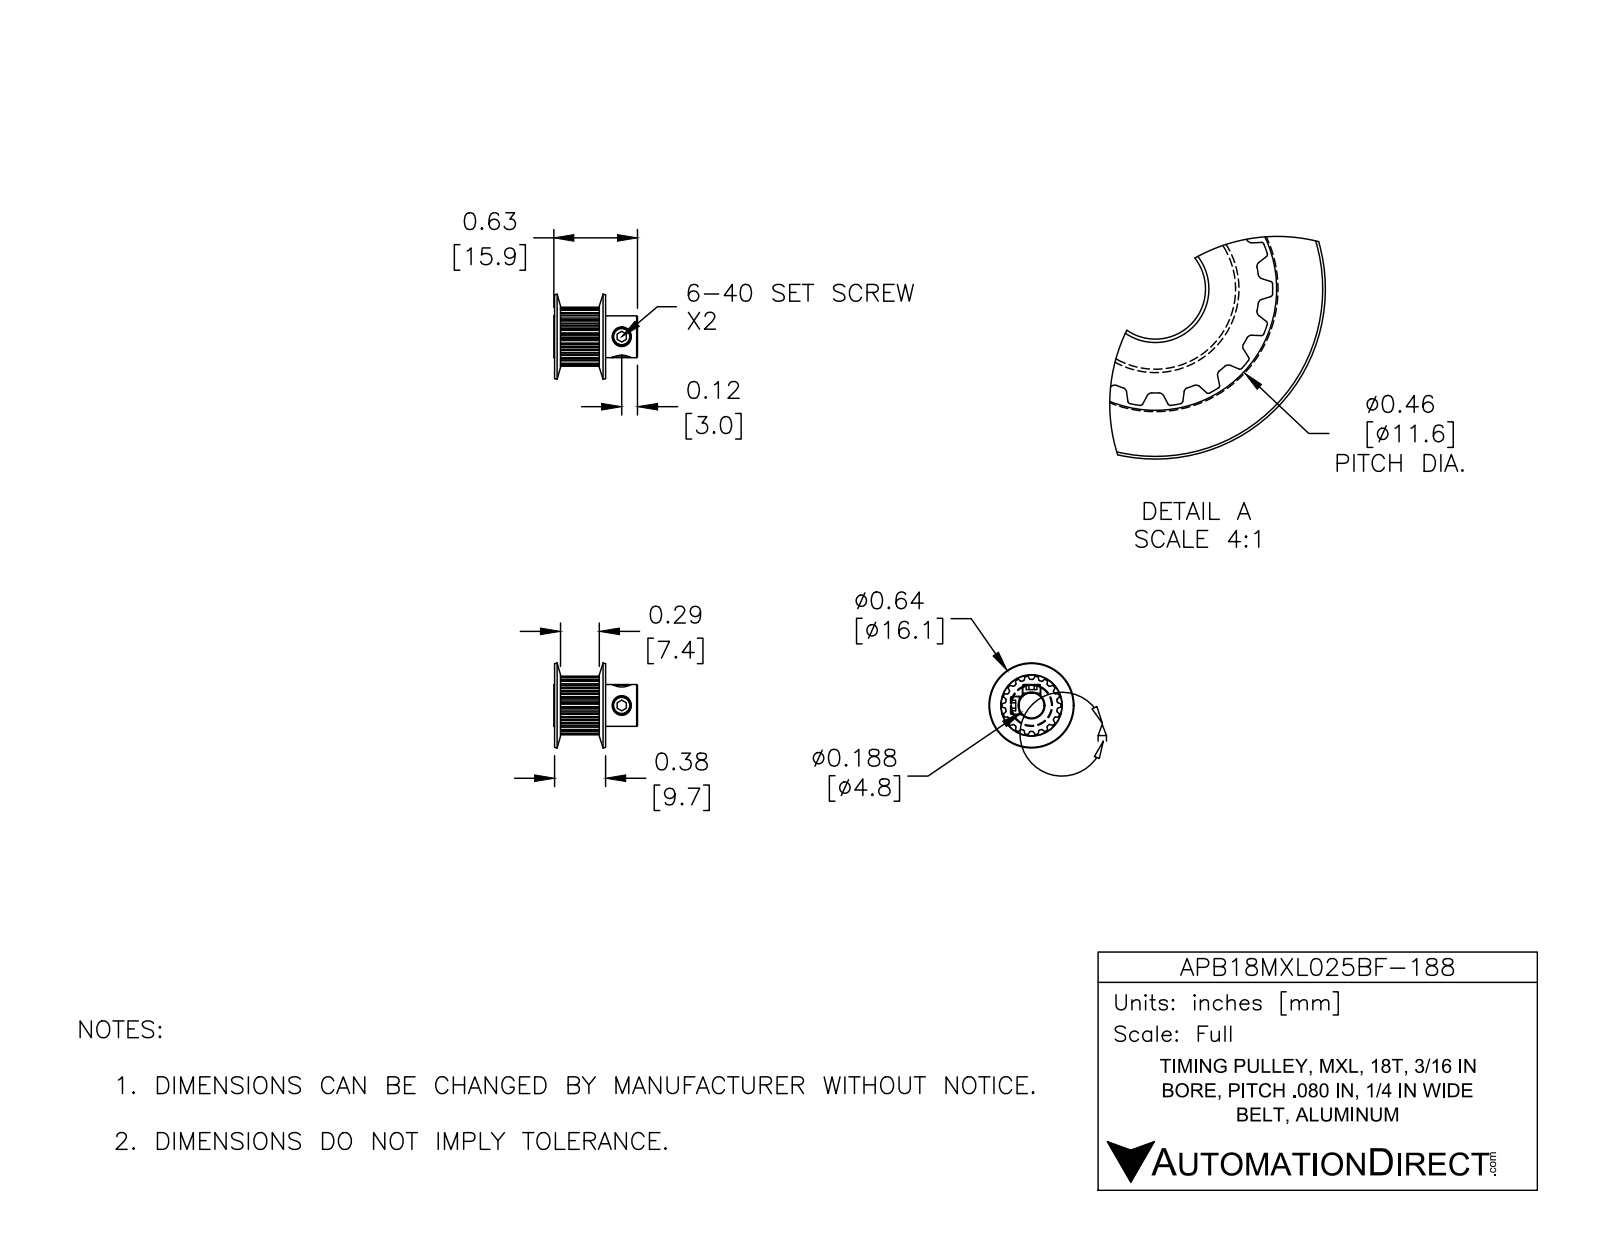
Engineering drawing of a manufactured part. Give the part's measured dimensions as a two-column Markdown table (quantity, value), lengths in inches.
| quantity | value |
| --- | --- |
| part name | APB18MXL025BF-188 |
| STEP written by | SolidWorks 2016 (AUTOMOTIVE_DESIGN) |
| units | inches |
| bodies | 3 solids, 221 faces (60 planar, 135 cylindrical, 26 other) |
| overall size | 0.635 × 0.635 × 0.625 |
| volume | 0.058 in³ |
| surface area | 2.306 in² |
| round holes (diameter × count) | 0.138 × 2, 0.187 × 1 |
| round bosses / shafts (diameter × count) | 0.13 × 2, 0.312 × 1 |
| partial cylindrical surfaces (radius × count) | 0.005 × 36, 0.009 × 36, 0.194 × 1, 0.219 × 1 |
| main face-to-face distances | 0.16, 0.339, 0.025, 0.364, 0.625, 0.6, 0.261, 0.34, 0.315, 0.024 |
